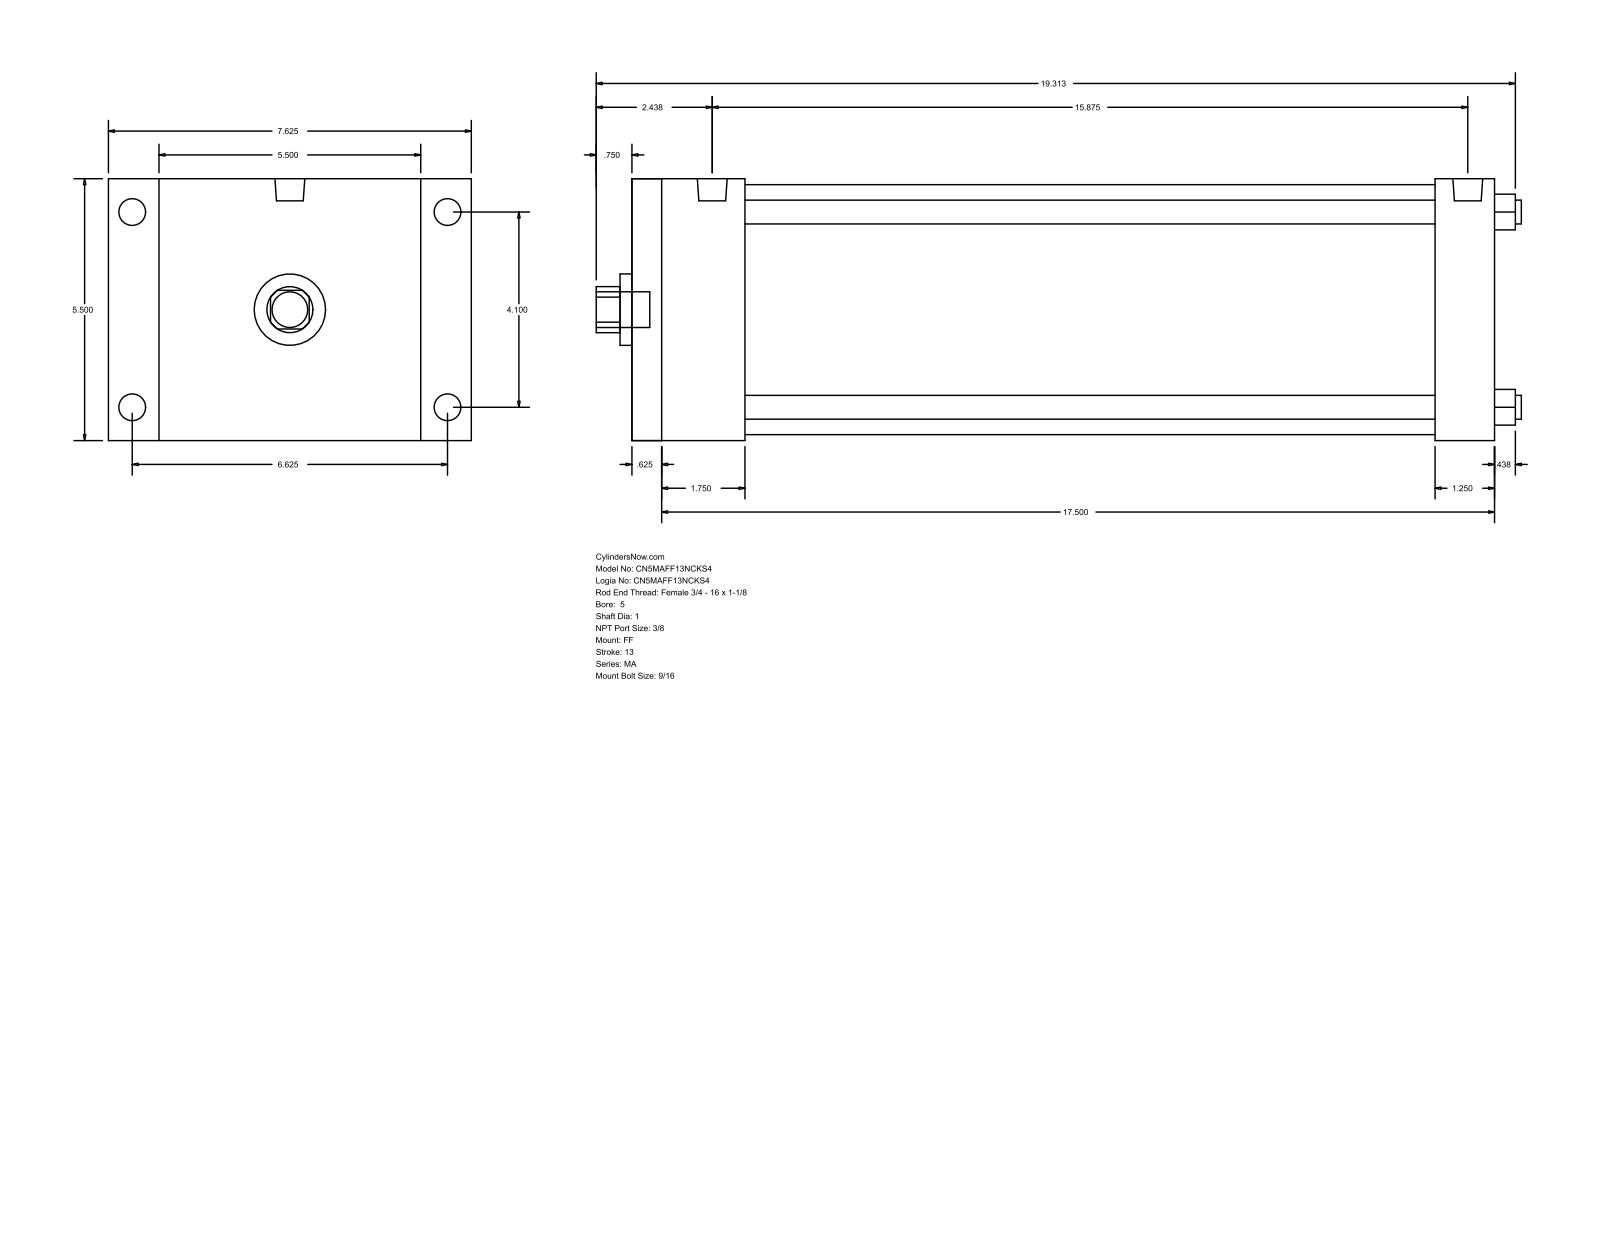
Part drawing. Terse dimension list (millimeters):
name: MA_FF__0500_1
written by: GSSL Pune (CONFIG_CONTROL_DESIGN)
unit: mm
bodies: 0 solids, 92 faces (64 planar, 28 cylindrical, 0 other)
size: 493.71 × 193.68 × 139.7
holes: 4× ⌀12.7, 1× ⌀25.4, 1× ⌀38.1, 1× ⌀133.35
bosses: 4× ⌀14.29, 4× ⌀11.11, 2× ⌀15.93, 1× ⌀19.05
rounds: 1× R12.29
face distances: 139.7, 460.38, 15.87, 444.51, 428.63, 412.76, 31.75, 60.33, 44.46, 368.3
hole spacings: 73.64, 104.14, 147.28
